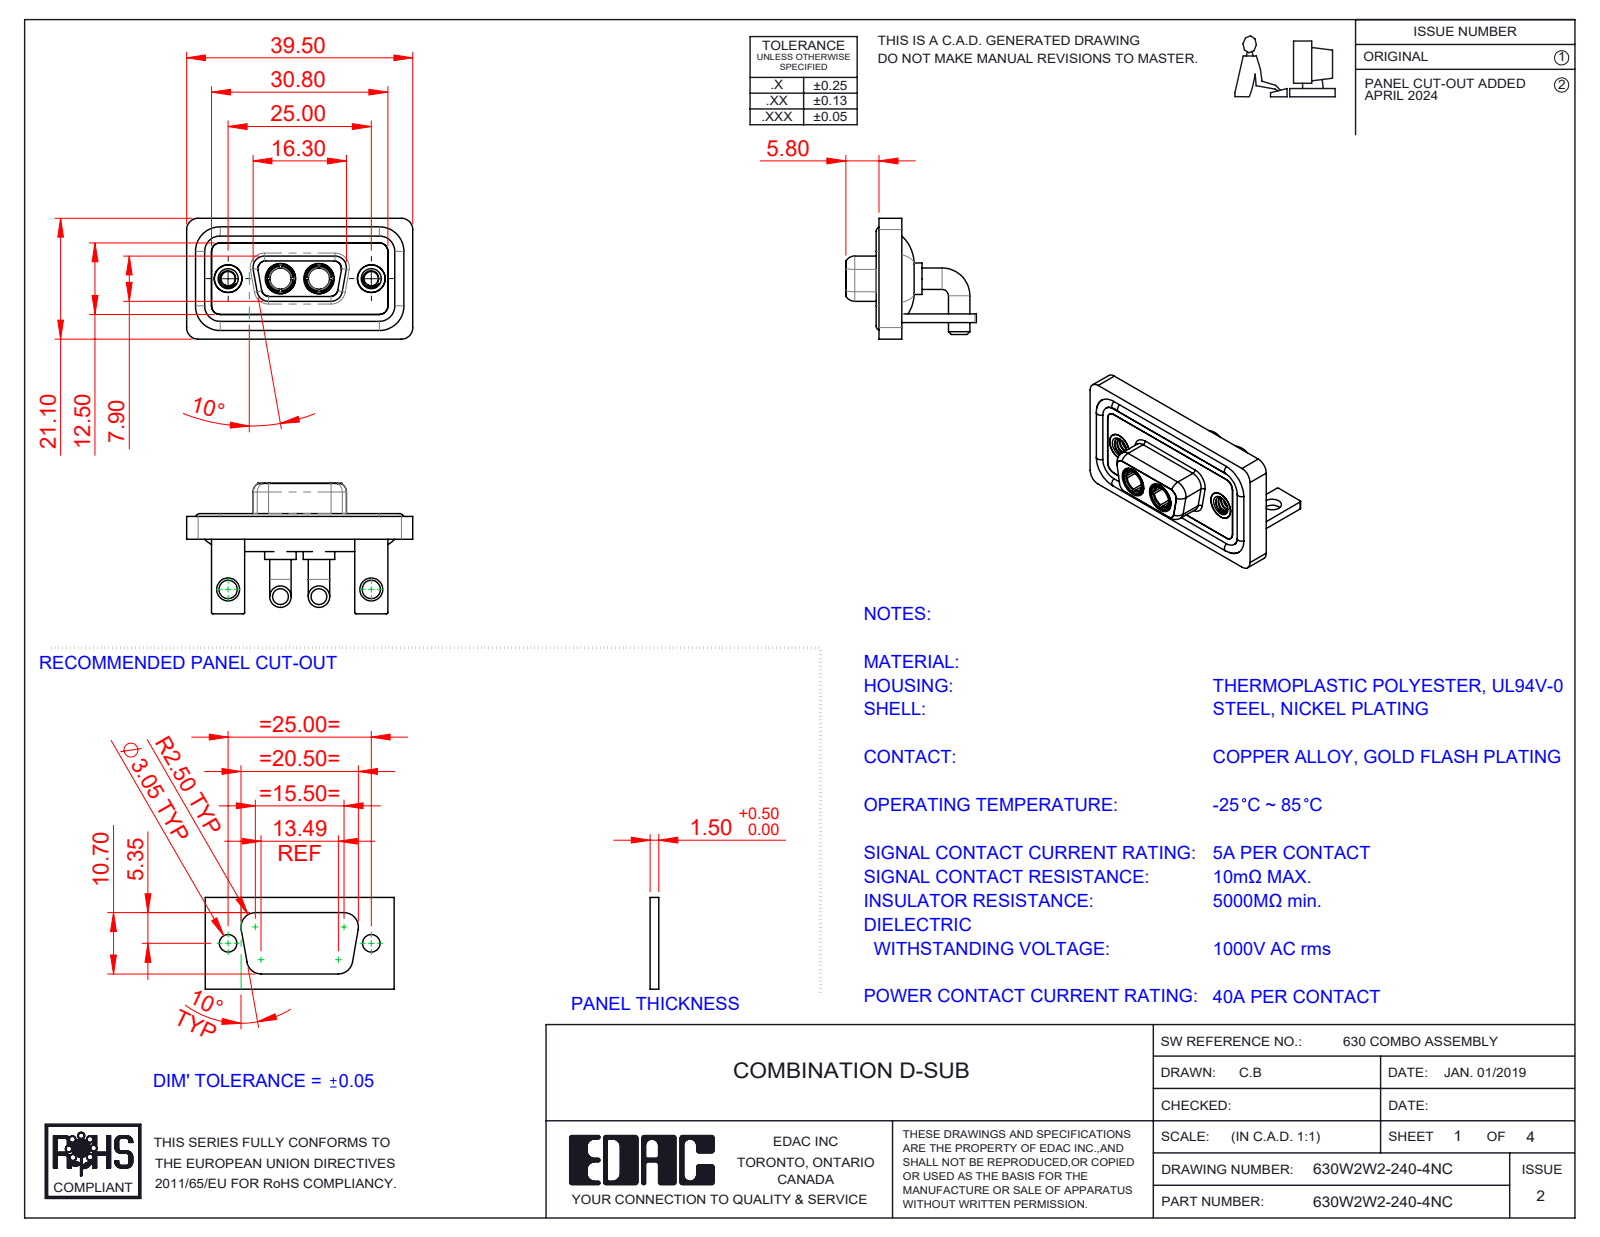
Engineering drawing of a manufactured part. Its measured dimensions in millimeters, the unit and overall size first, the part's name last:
Units: millimetres
Overall size (bounding box): 39.5 × 22.8 × 21.1
Round holes (diameter × count): ⌀4.85 ×4, ⌀2.5 ×2, ⌀3.2 ×2, ⌀3.7 ×2, ⌀4 ×2, ⌀4.05 ×2, ⌀5 ×2, ⌀5.3 ×2
Round bosses / shafts (diameter × count): ⌀3.75 ×4, ⌀1.6 ×4, ⌀5.5 ×2, ⌀5.2 ×2, ⌀4.96 ×2, ⌀4.95 ×2, ⌀4.8 ×2, ⌀4.75 ×2
Partial cylindrical surfaces — rounded edges, fillets, slot ends (radius × count): R2 ×19, R1.5 ×18, R0.25 ×16, R1.35 ×8, R1.6 ×8, R0.5 ×5, R0.6 ×4, R0.65 ×4
Main face-to-face distances: 0.4, 2.9, 1.5, 1.8, 1.1, 3.7, 0.8, 2.5, 1.6, 3.1
Hole centre spacings: 9.14, 15.86, 25, 6.72
Volume: 5 321 mm³ · Surface area: 8 612 mm²
Bodies: 13 solids, 584 faces (183 planar, 260 cylindrical, 141 other)
Part name (STEP PRODUCT): 630Combo Housing_2W2; 630Combo Threaded Rivet_A; Power Socket_40A RA; 630Combo Shell Front_09 Contacts (+4 more)
STEP written by: SolidWorks 2023 (CONFIG_CONTROL_DESIGN)
